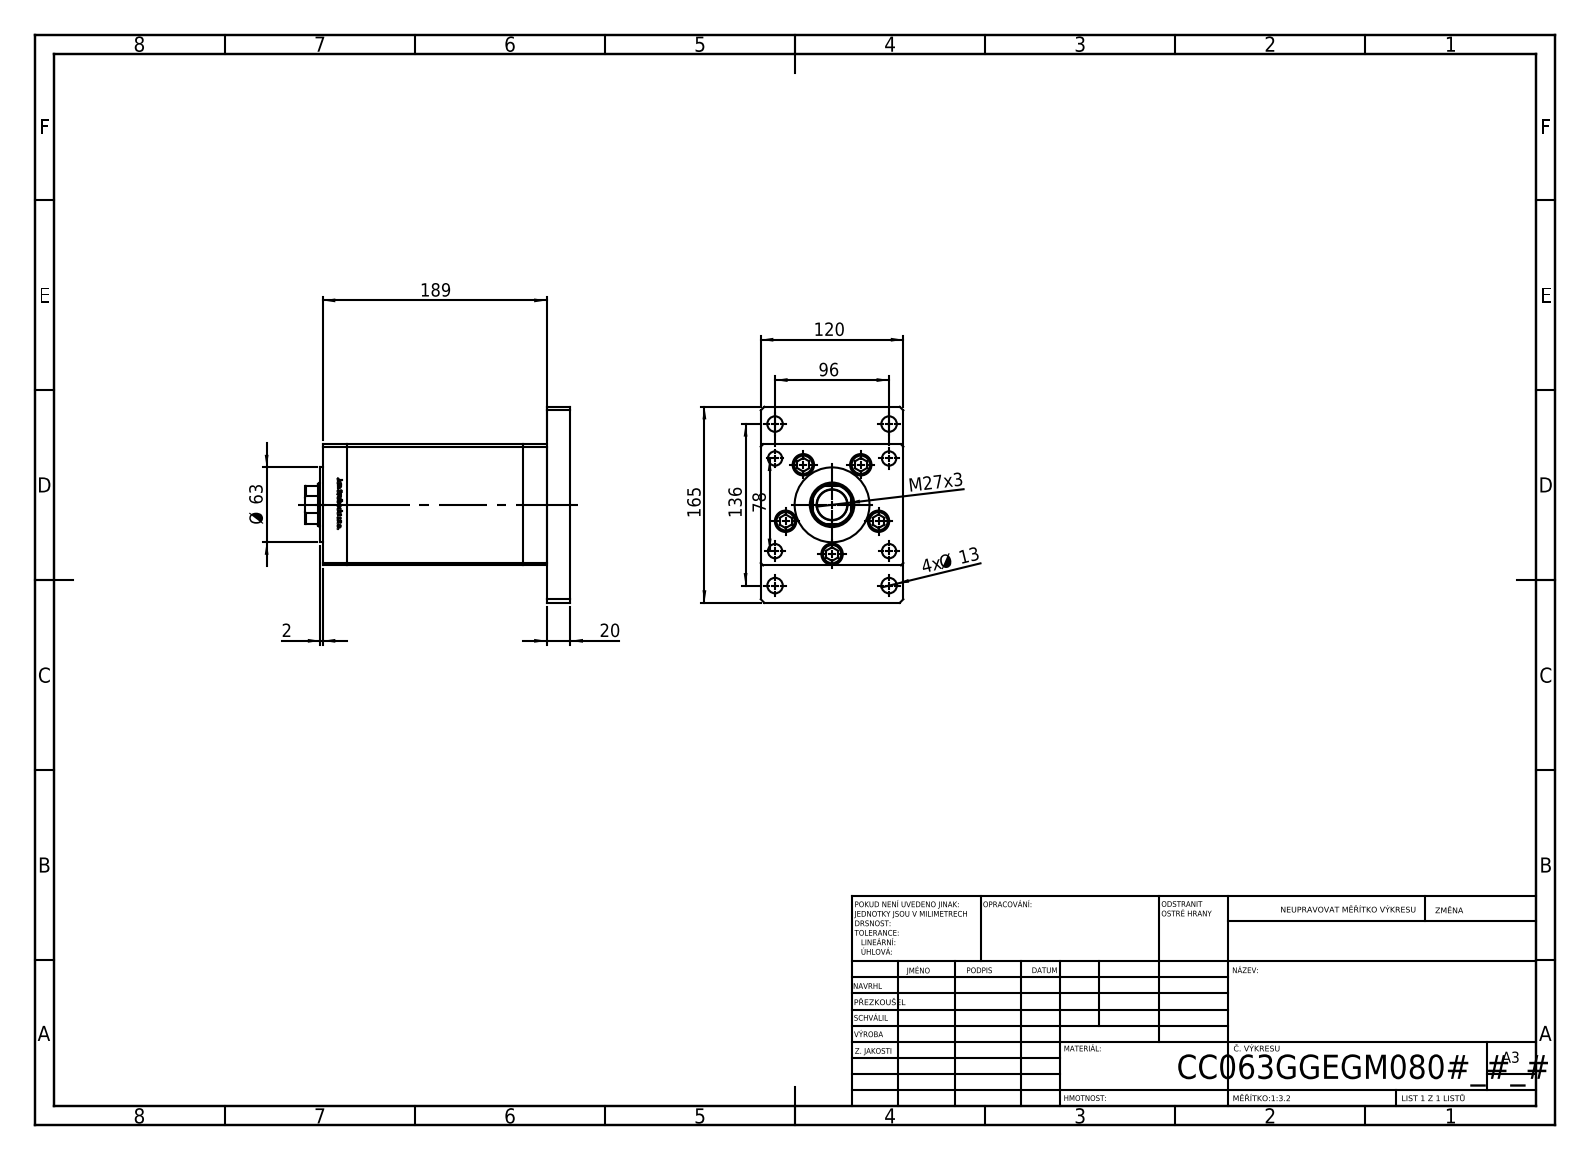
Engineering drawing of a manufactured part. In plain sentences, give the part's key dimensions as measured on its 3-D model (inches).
The part is named "V220C_F; V220C BACK_G; ALLEN BOLT; V220C_G_MIDDLE (+2 more)". Its 3-D file was written by "SolidWorks 2019 (CONFIG_CONTROL_DESIGN)". It is 19 solids with 1313 faces: 518 planar, 189 cylindrical and 606 other. Overall it measures 8.799 by 6.496 by 4.724 inches. Its volume is 146.1 cubic inches and its surface area 493.6 square inches. Round holes: 9 of diameter 0.472, 5 of diameter 0.531, 5 of diameter 0.709, 4 of diameter 0.512, 4 of diameter 0.669, 2 of diameter 0.079, 2 of diameter 0.518, 1 of diameter 1.004, 1 of diameter 1.417, 1 of diameter 1.476, 1 of diameter 3.268. Round bosses or shafts: 9 of diameter 0.315, 5 of diameter 0.669, 1 of diameter 2.48. Partial cylindrical surfaces (rounded edges, fillets, slot ends): 2 of radius 0.037, 1 of radius 0.689. The main face-to-face distances are 0.787, 6.634, 4.724, 7.421, 4.016, 5.846, 1.575, 0.079, 7.343, 0.709. The hole center spacings are 1.634, 1.142, 2.435, 3.277, 3.78, 3.948, 4.213, 5.659.
